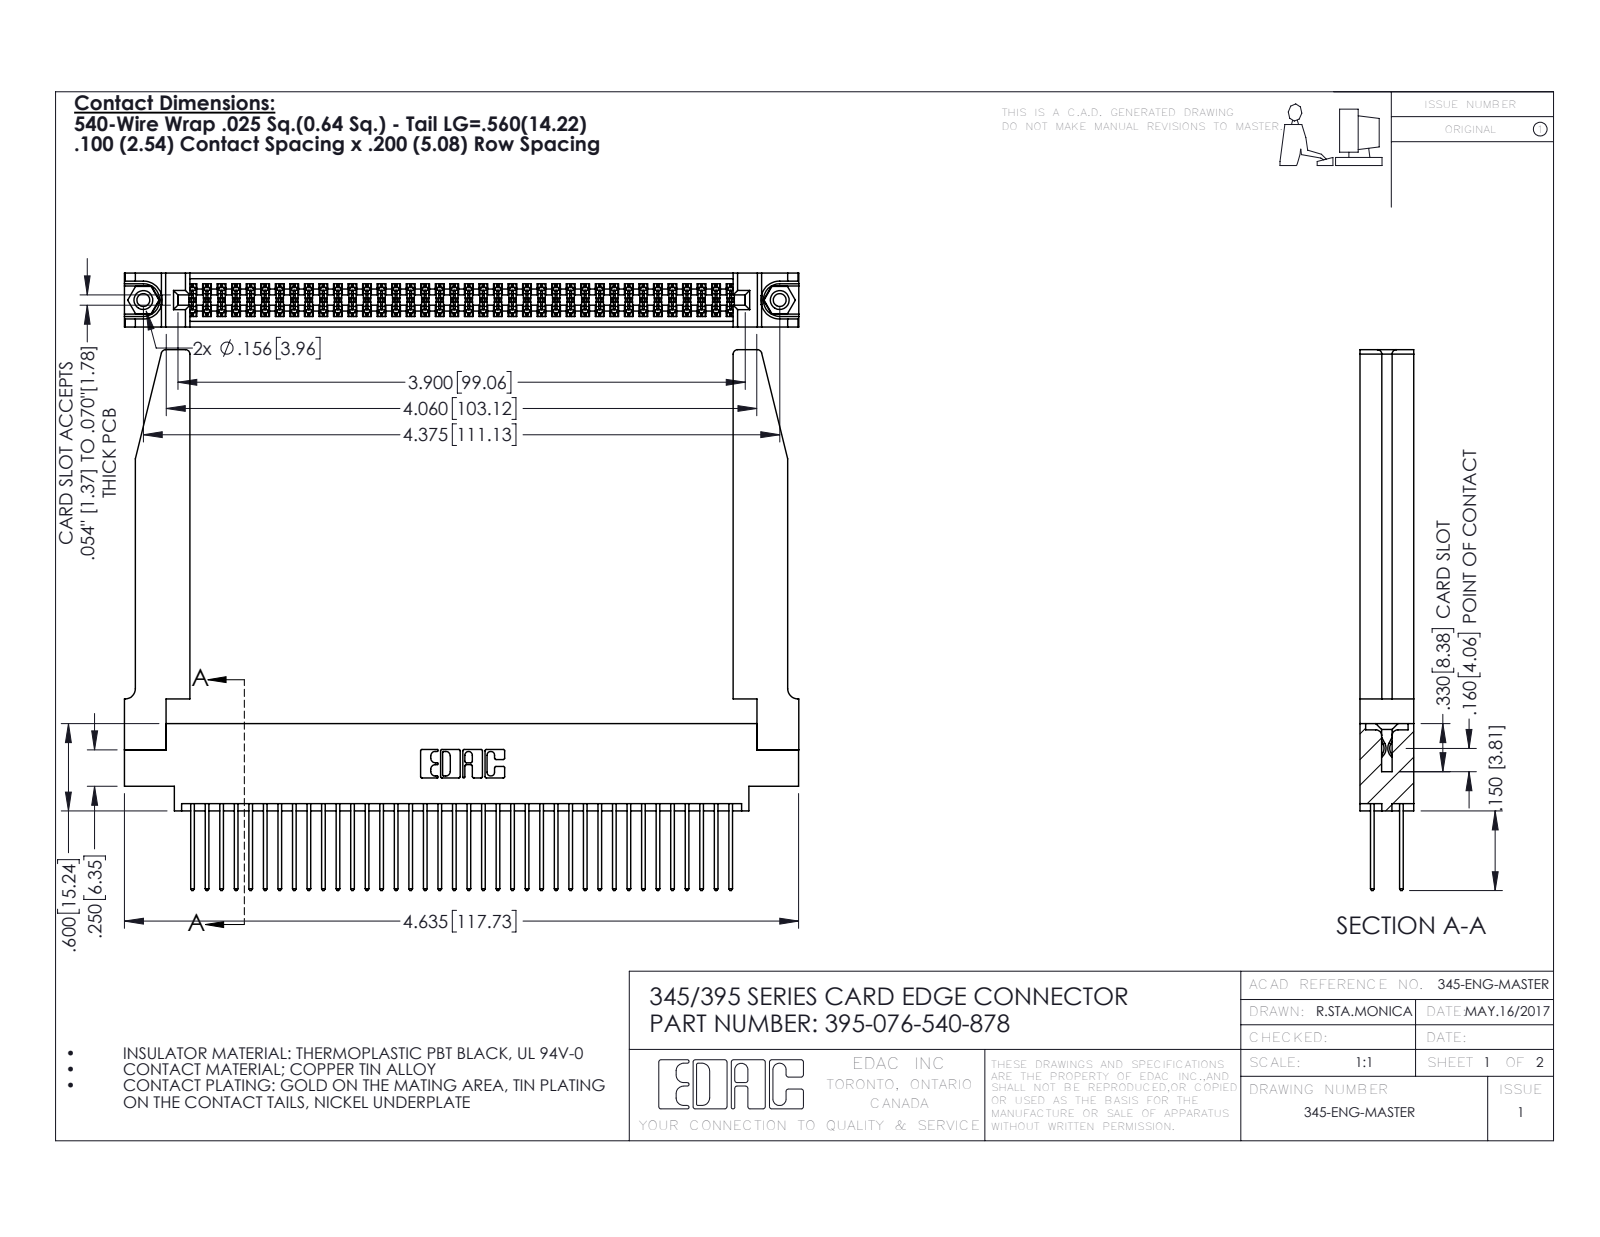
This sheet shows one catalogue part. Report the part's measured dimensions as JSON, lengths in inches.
{"part_name": "345 Part_0.170 Offset - 0.156 Dia-TH; 395-076-540-878; 345-250-001_345-250-001-102; 345-292-001_345-293-140 (+1 more)", "step_written_by": "SolidWorks 2016 (CONFIG_CONTROL_DESIGN)", "units": "inches", "bodies": {"solids": 81, "faces": 4164, "planar": 2734, "cylindrical": 1378, "other": 52}, "overall_size": [4.636, 3.717, 0.37], "volume_in3": 1.181, "surface_area_in2": 39.3, "round_holes": [[0.089, 2], [0.125, 2], [0.156, 2], [0.064, 1]], "round_bosses_or_shafts": [[0.155, 2]], "partial_cylinders_radius": [[0.006, 114], [0.01, 76], [0.01, 22], [0.03, 8], [0.007, 6], [0.031, 6], [0.026, 3], [0.014, 2]], "face_to_face_distances": [0.072, 0.298, 0.37, 0.098, 0.272, 0.025, 0.2, 0.225, 0.175, 0.148], "hole_center_spacings": [0.27, 4.139, 4.375]}
